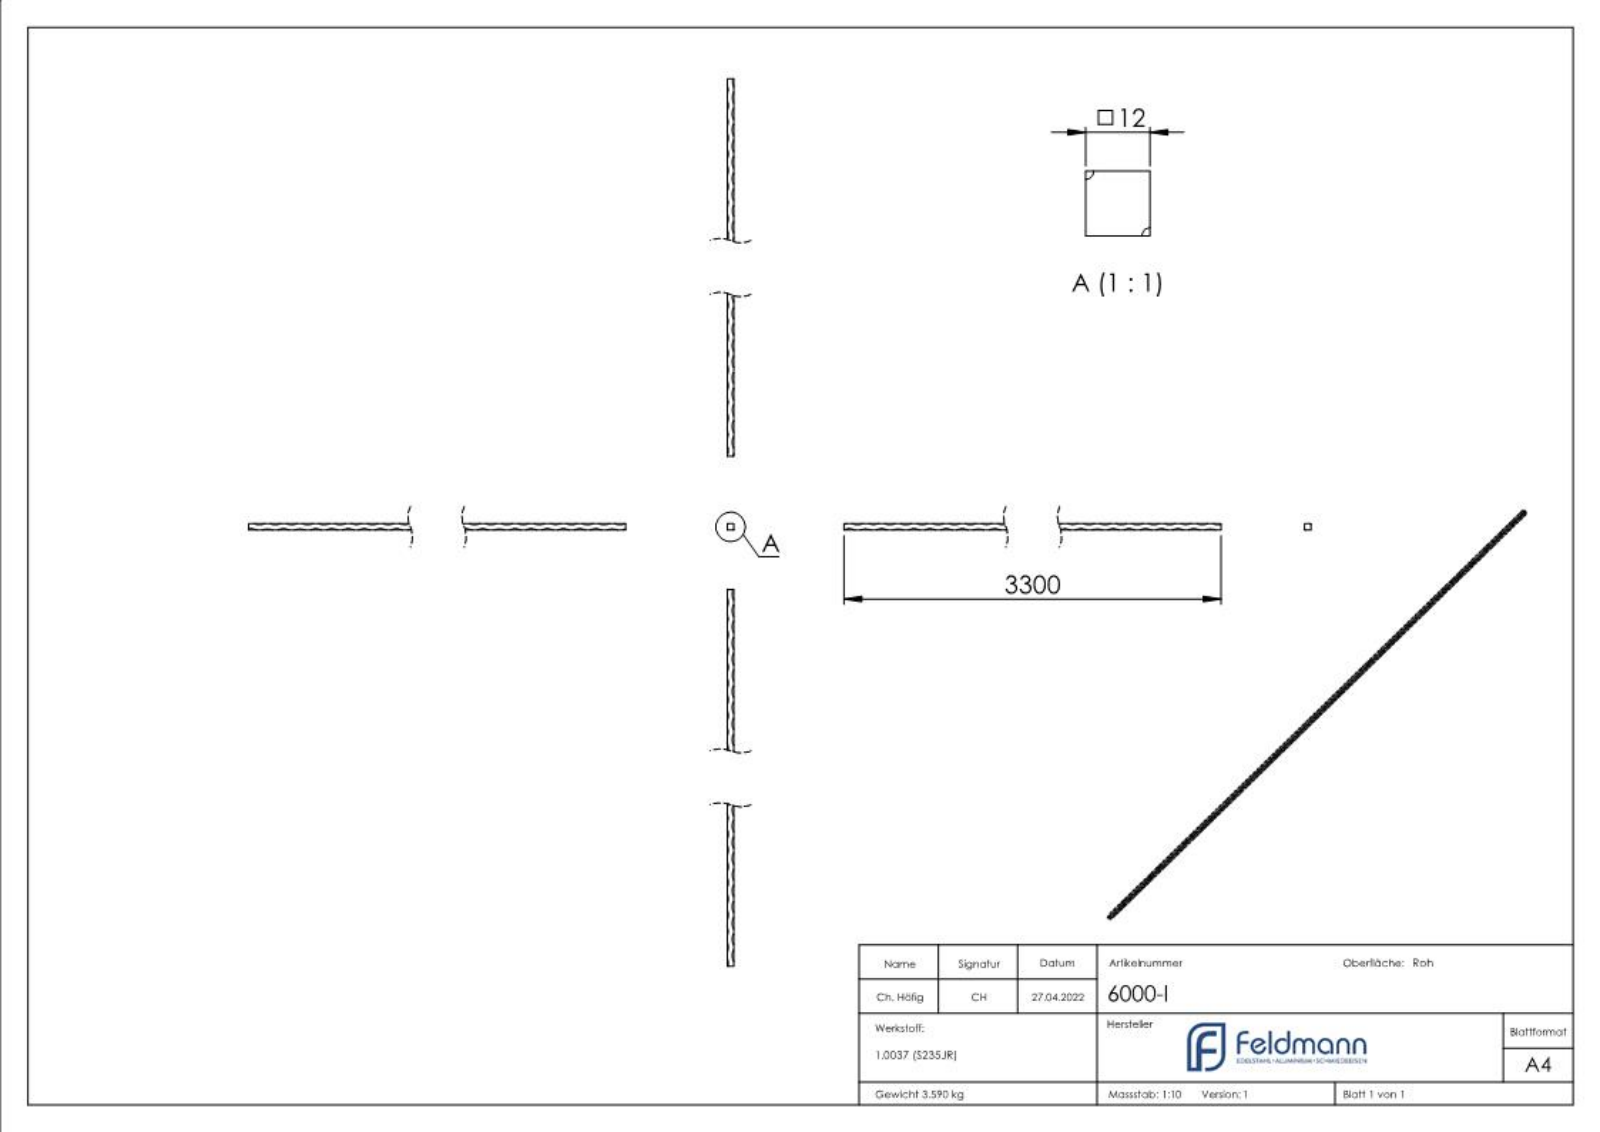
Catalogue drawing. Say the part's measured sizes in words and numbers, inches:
The part is named "6000-I". Its 3-D file was written by "SolidWorks 2018 (CONFIG_CONTROL_DESIGN)". It is 1 solid with 661 faces: 115 planar, 0 cylindrical and 546 other. Overall it measures 129.921 by 0.472 by 0.472 inches. Its volume is 28.09 cubic inches and its surface area 238.6 square inches. The main face-to-face distances are 0.472, 129.921, 0.469, 0.013, 0.072, 0.129, 0.134, 0.139, 0.142, 0.114.
